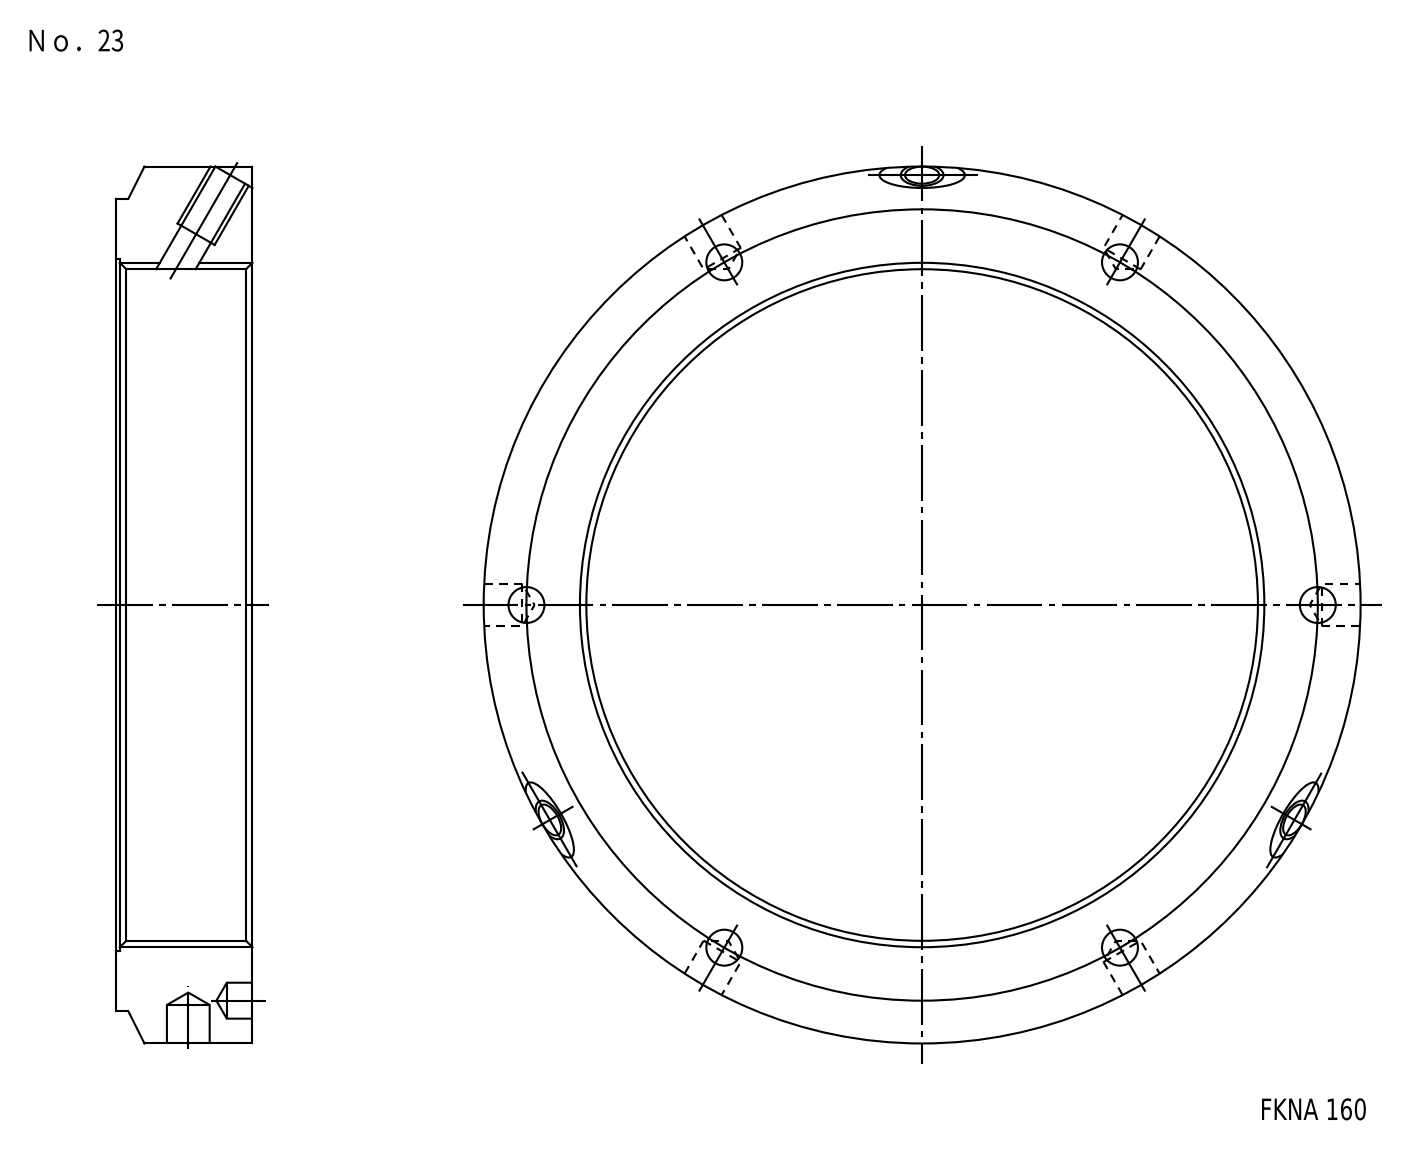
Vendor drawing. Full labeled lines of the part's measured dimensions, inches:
Part name (STEP PRODUCT): FKD FKNA160
STEP written by: Autodesk Inventor LT (CONFIG_CONTROL_DESIGN)
Units: inches
Bodies: 1 solid, 44 faces (6 planar, 25 cylindrical, 13 other)
Overall size (bounding box): 8.071 × 8.071 × 1.26
Volume: 23.51 in³ · Surface area: 99.86 in²
Round holes (diameter × count): ⌀0.331 ×6, ⌀0.33 ×3, ⌀0.394 ×3, ⌀0.402 ×3, ⌀6.299 ×1, ⌀6.378 ×1
Round bosses / shafts (diameter × count): ⌀8.071 ×1, ⌀7.48 ×1
Partial cylindrical surfaces — rounded edges, fillets, slot ends (radius × count): R0.787 ×3
Main face-to-face distances: 1.26, 0.059, 1.201
Hole centre spacings: 3.642, 6.308, 7.283
